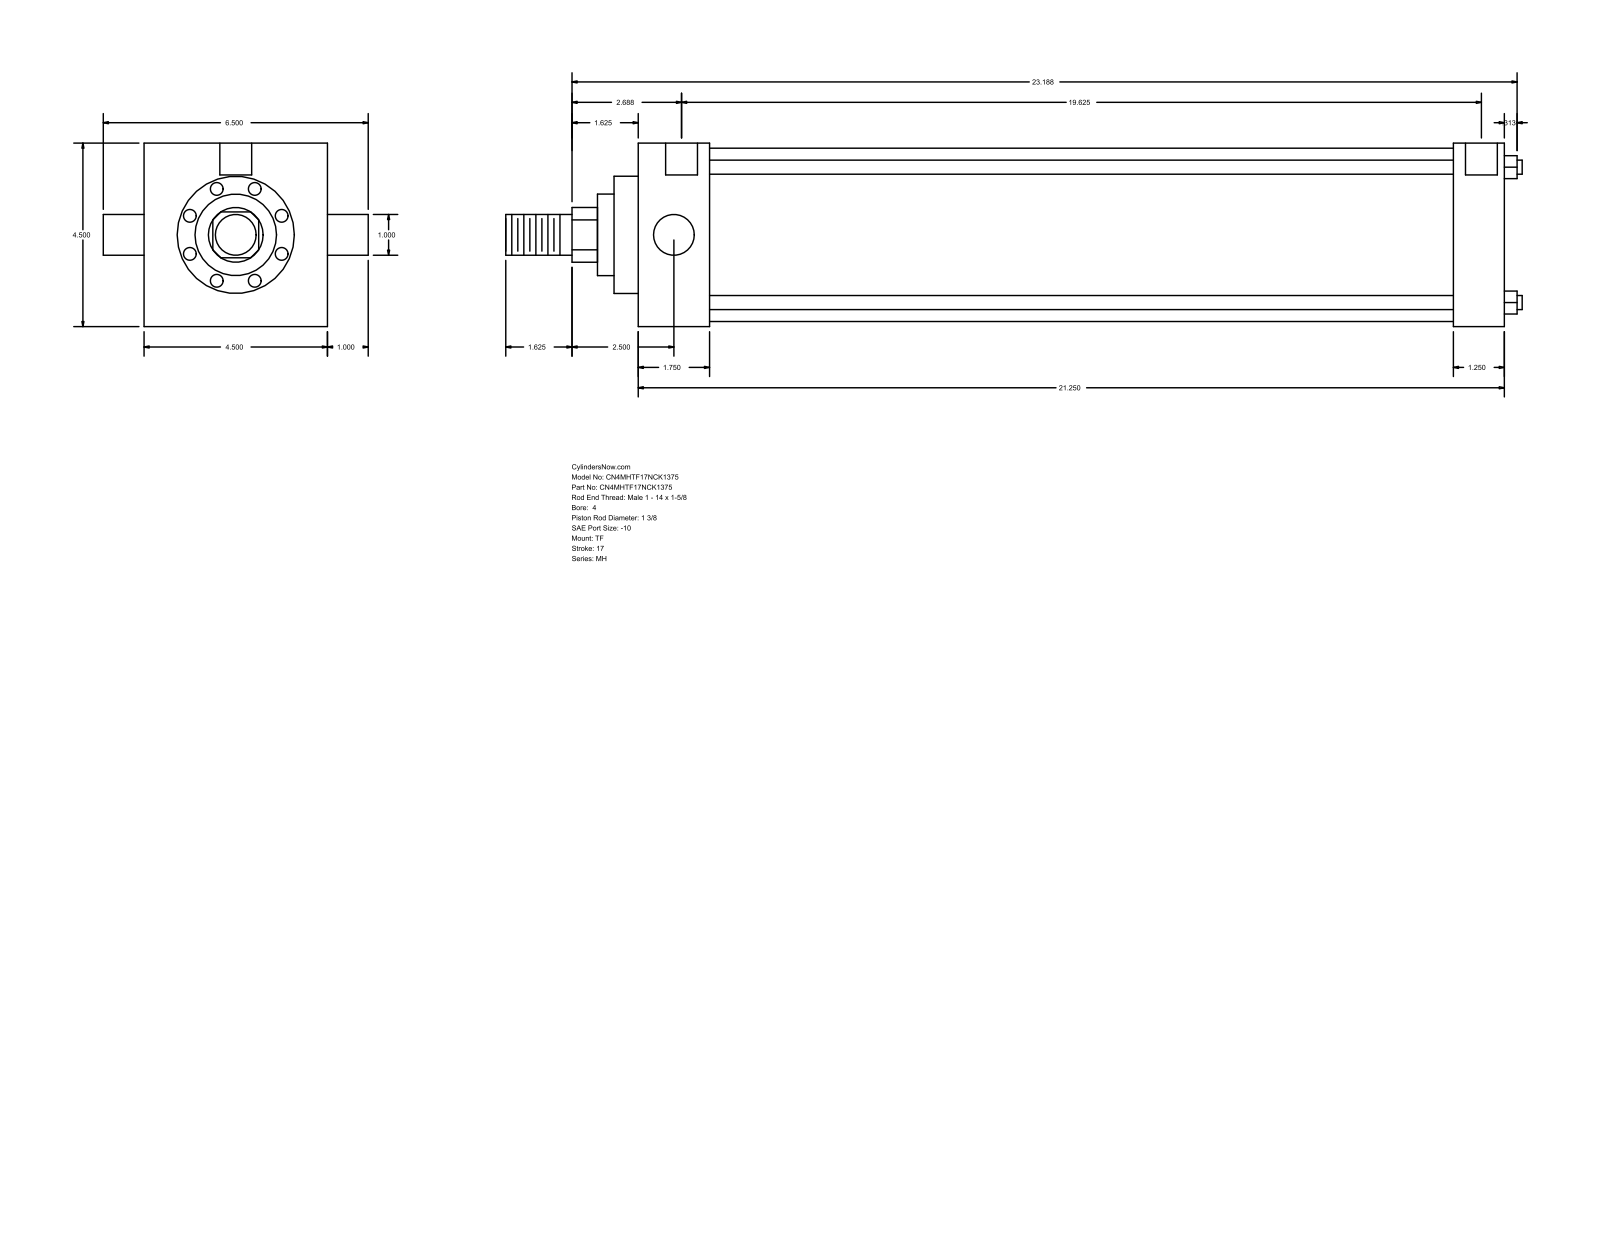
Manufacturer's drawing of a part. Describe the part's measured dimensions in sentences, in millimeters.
The part is named "MH_TF__0400_1.375". Its 3-D file was written by "GSSL Pune (CONFIG_CONTROL_DESIGN)". It is 0 solids with 86 faces: 61 planar, 25 cylindrical and 0 other. Overall it measures 633.41 by 165.1 by 114.3 millimeters. Round holes: 3 of diameter 8.73, 2 of diameter 19.84. Round bosses or shafts: 4 of diameter 8.76, 2 of diameter 25.4, 1 of diameter 107.95, 1 of diameter 73.03, 1 of diameter 50.8, 1 of diameter 34.92. Partial cylindrical surfaces (rounded edges, fillets, slot ends): 1 of radius 17.06. The main face-to-face distances are 114.3, 539.75, 44.45, 495.3, 508, 463.55, 31.75, 15.08, 59.53, 523.08. The hole center spacings are 1.59, 500.07, 498.48, 501.66.
